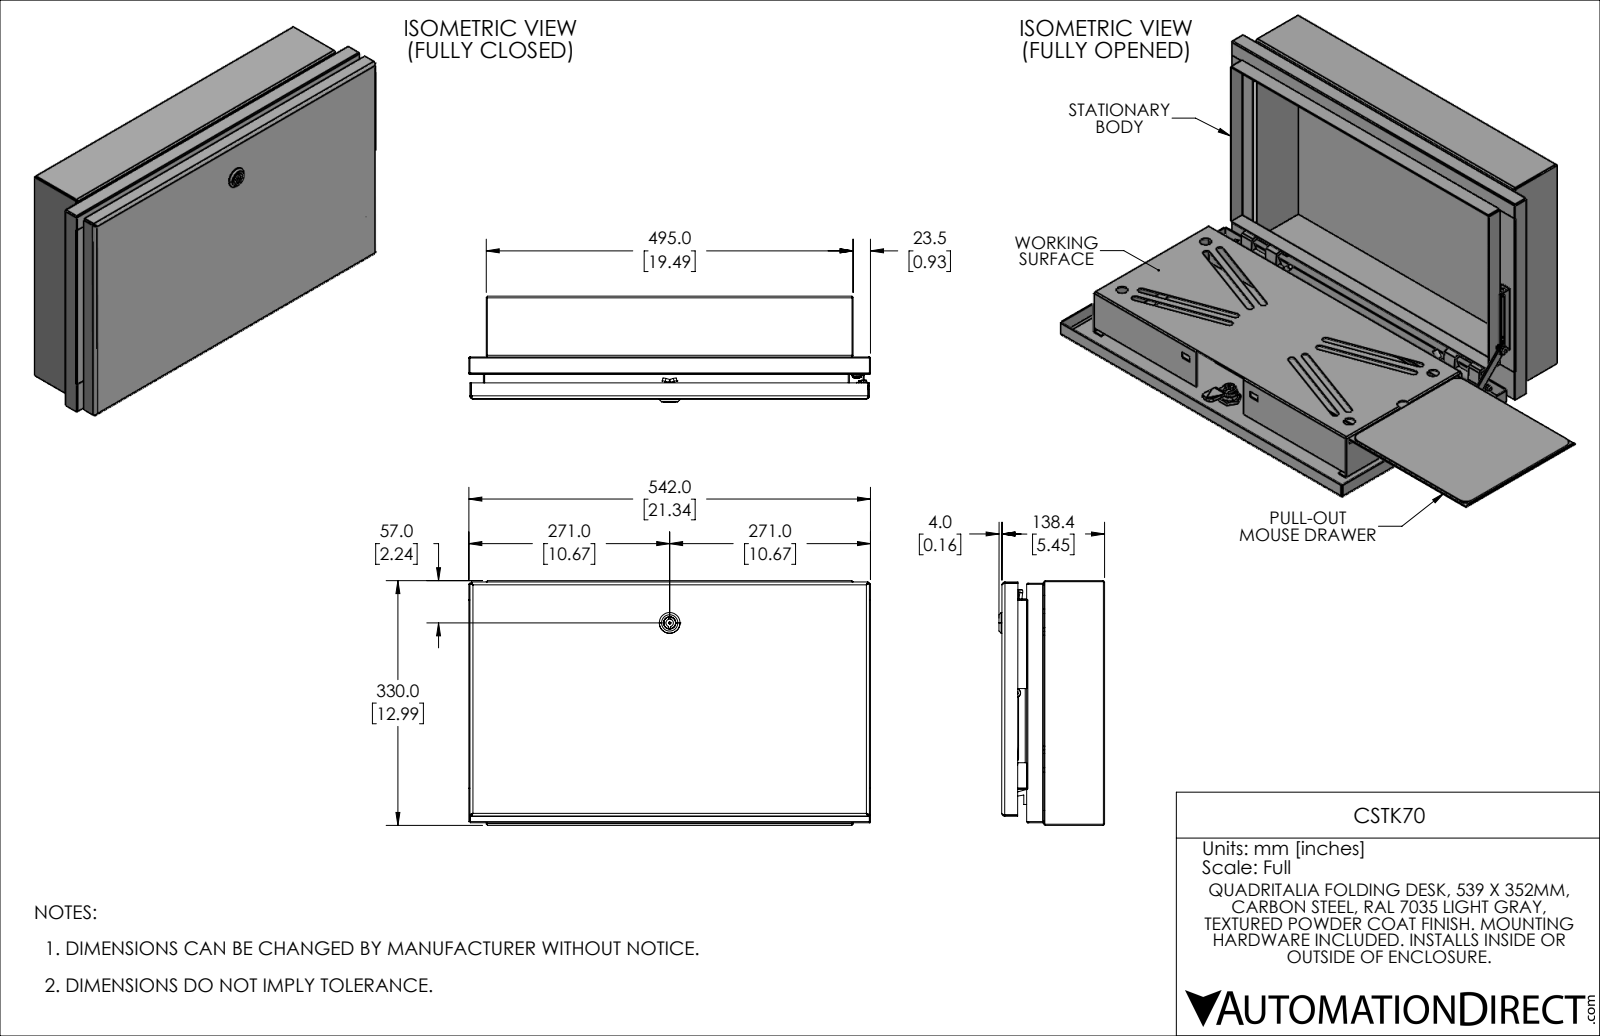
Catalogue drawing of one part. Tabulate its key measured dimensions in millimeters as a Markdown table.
| quantity | value |
| --- | --- |
| part name | CSTK70 - FULLY CLOSED |
| STEP written by | SolidWorks 2021 (AUTOMOTIVE_DESIGN) |
| units | millimeters |
| bodies | 42 solids, 1400 faces (656 planar, 504 cylindrical, 240 other) |
| overall size | 542 × 330 × 142.5 |
| volume | 1 573 000 mm³ |
| surface area | 2 028 000 mm² |
| round holes (diameter × count) | 7 × 10, 5 × 8, 6 × 7, 6.2 × 7, 0.3 × 4, 16 × 4, 7.2 × 3, 3 × 1, 4.1 × 1, 10 × 1, 10.2 × 1, 16.1 × 1 |
| round bosses / shafts (diameter × count) | 12 × 5, 7 × 3, 6 × 2, 28 × 1, 19.8 × 1, 16 × 1, 15.2 × 1, 12.8 × 1 |
| partial cylindrical surfaces (radius × count) | 0.5 × 58, 2 × 20, 5 × 17, 1.5 × 16, 1.5 × 15, 0.2 × 8, 4 × 8, 2.3 × 5 |
| main face-to-face distances | 1.5, 61.3, 5.3, 66.5, 59.8, 62.8, 103.5, 3.8, 65, 6.8 |
| hole center spacings | 310, 10, 193.7, 365.5, 496.1, 27.5, 159.6, 282.5 |
